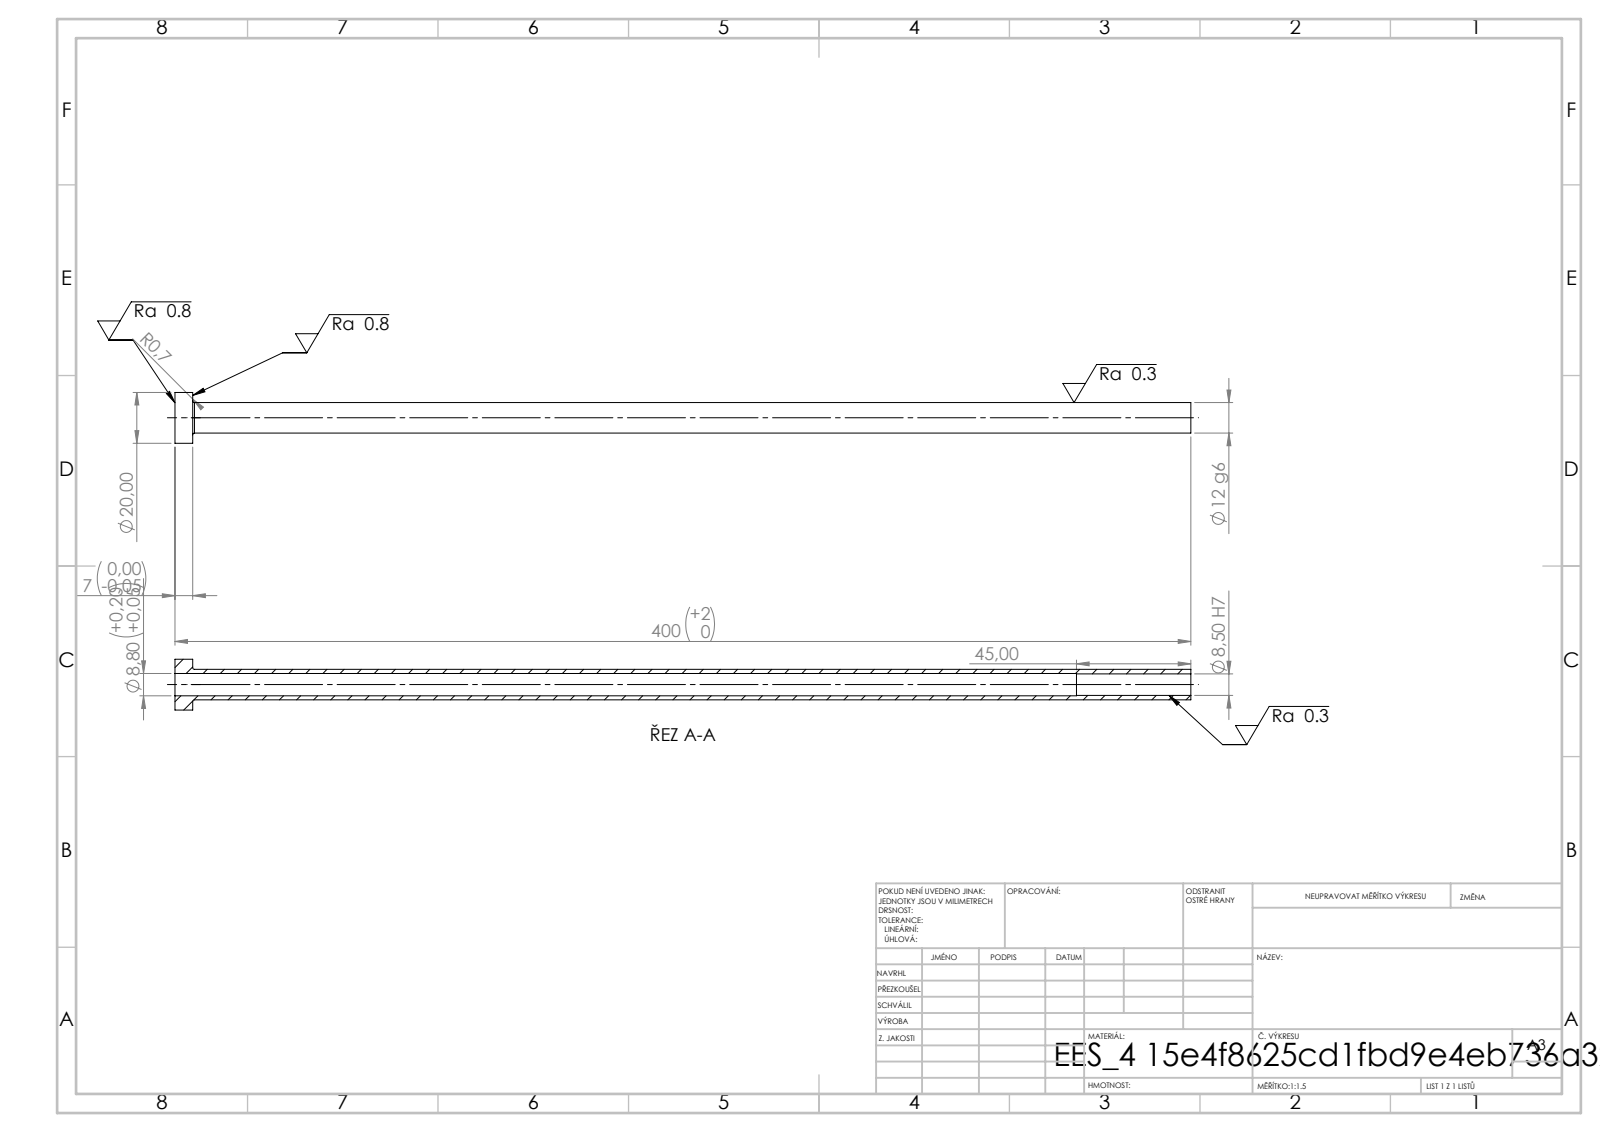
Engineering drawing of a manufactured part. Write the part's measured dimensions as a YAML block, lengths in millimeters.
step_written_by: "SolidWorks 2019 (CONFIG_CONTROL_DESIGN)"
units: millimeters
bodies: {solids: 1, faces: 14, planar: 4, cylindrical: 8, other: 2}
overall_size: [400, 20, 20]
volume: 22505
surface_area: 26775
round_holes:
  - {diameter: 8.5, count: 1}
  - {diameter: 8.8, count: 1}
round_bosses_or_shafts:
  - {diameter: 20, count: 1}
  - {diameter: 12, count: 1}
face_to_face_distances: [7, 400, 393, 355, 348, 45]
